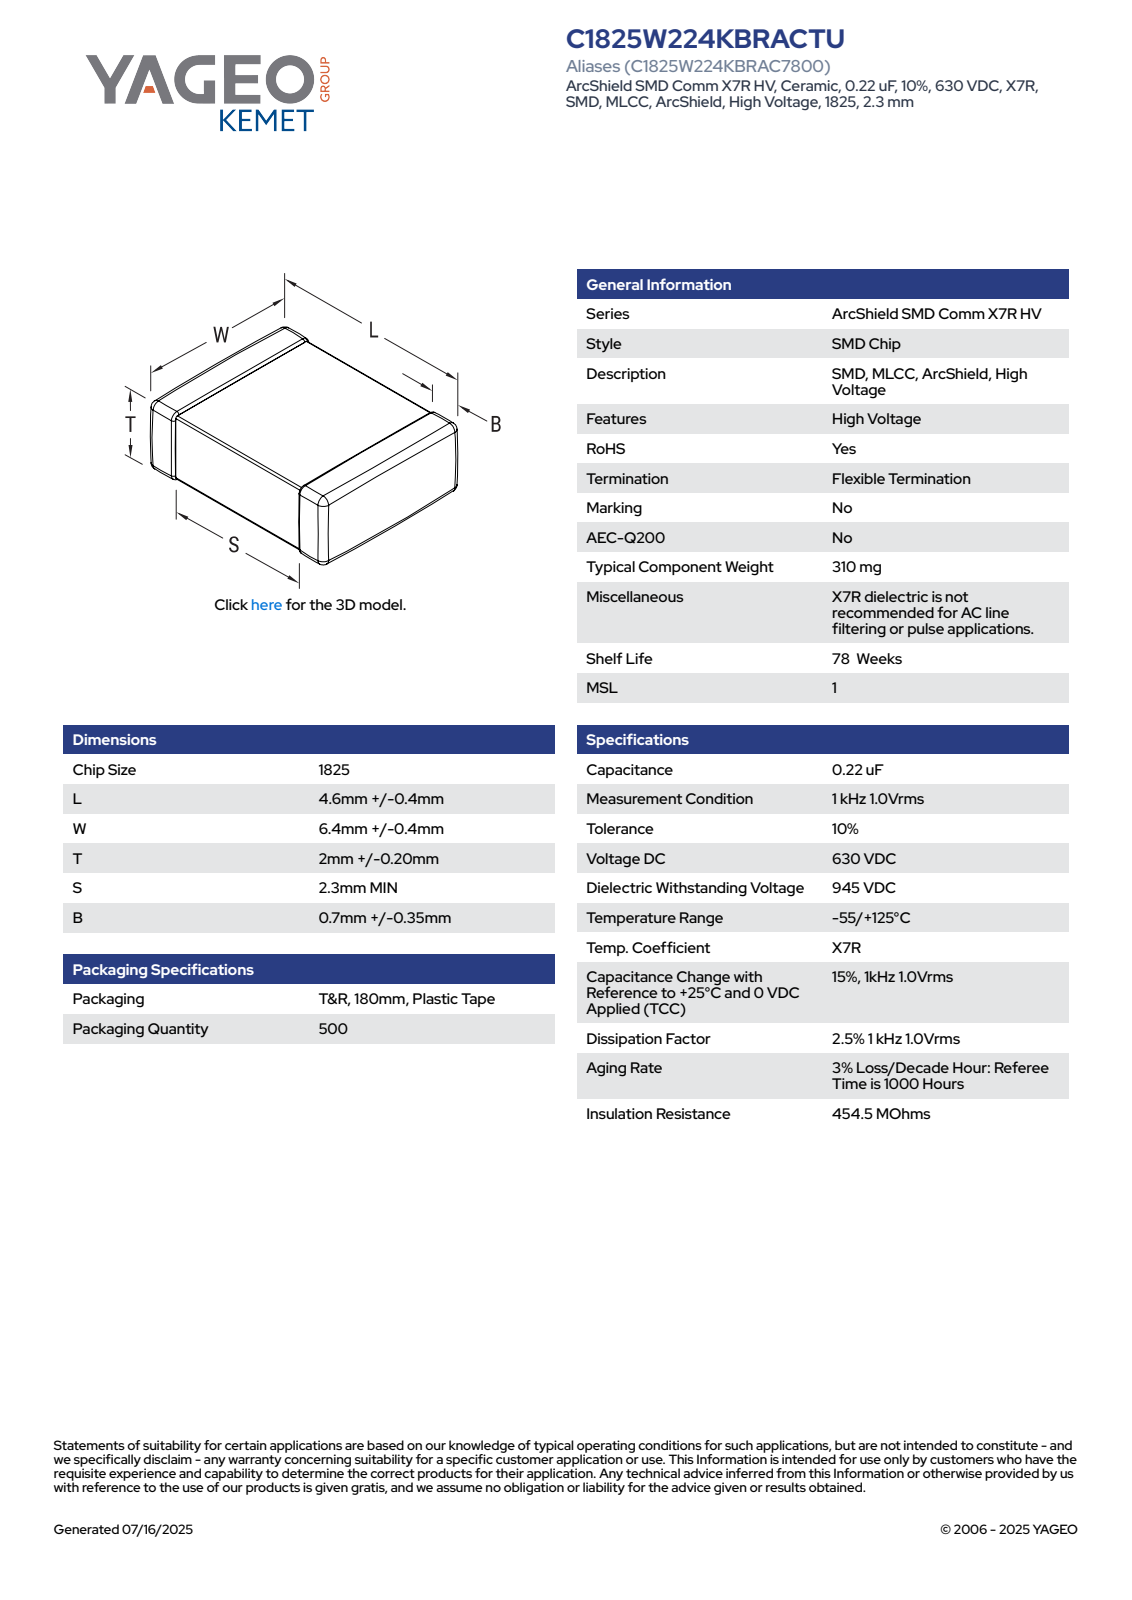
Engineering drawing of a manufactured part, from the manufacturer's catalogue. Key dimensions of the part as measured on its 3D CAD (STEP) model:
Part name (STEP PRODUCT): CCS_CCSTD_1825_L5W6.8T2.2B0.7
STEP written by: SolidWorks 2021 (AUTOMOTIVE_DESIGN)
Units: millimetres
Bodies: 4 solids, 121 faces (71 planar, 34 cylindrical, 16 other)
Overall size (bounding box): 6.8 × 5 × 2.2
Volume: 67 mm³ · Surface area: 122 mm²
Partial cylindrical surfaces — rounded edges, fillets, slot ends (radius × count): R0.14 ×24
Main face-to-face distances: 2.06, 1.92, 5, 2.2, 6.66, 6.52, 6.8, 1, 2.3, 1.7
